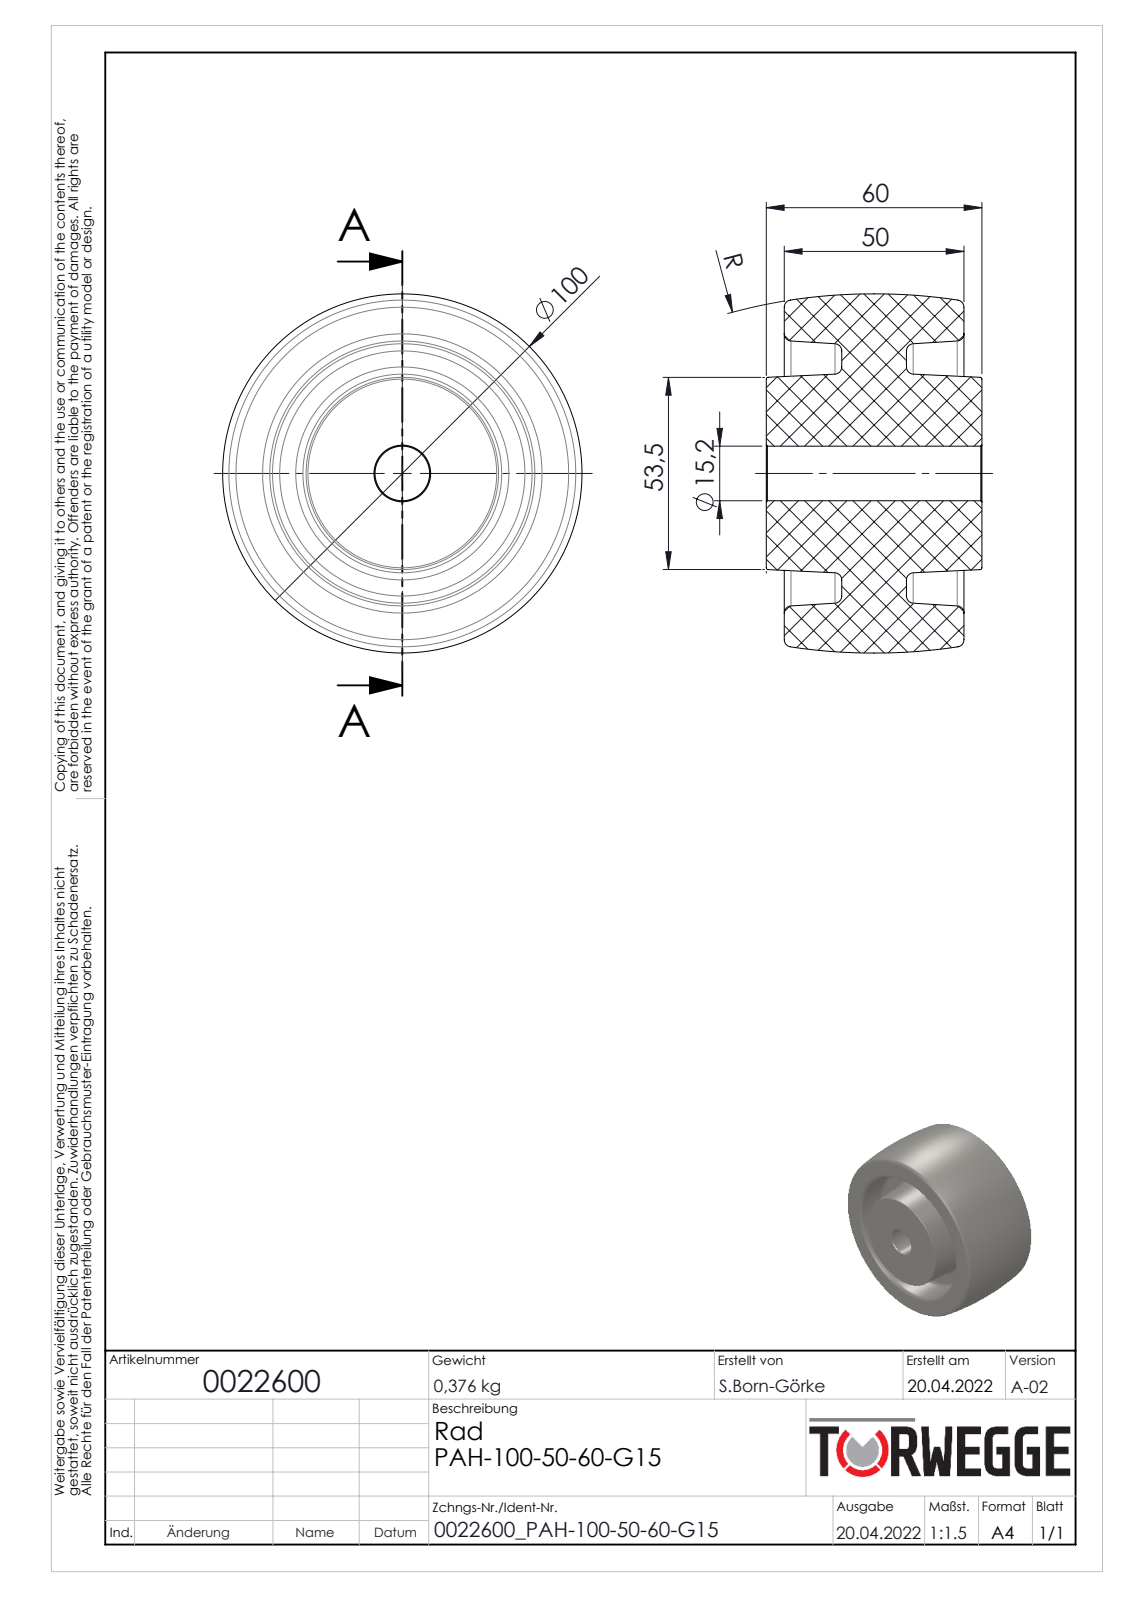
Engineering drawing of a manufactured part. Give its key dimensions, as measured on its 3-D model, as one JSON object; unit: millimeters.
{"part_name": "0022600", "step_written_by": "SolidWorks 2020 (AUTOMOTIVE_DESIGN)", "units": "millimeters", "bodies": {"solids": 1, "faces": 44, "planar": 6, "cylindrical": 2, "other": 36}, "overall_size": [100, 100, 60], "volume_mm3": 335674, "surface_area_mm2": 44918, "round_holes": [[15.2, 1]], "face_to_face_distances": [5, 55, 50, 60, 21, 39, 16, 34, 18]}
